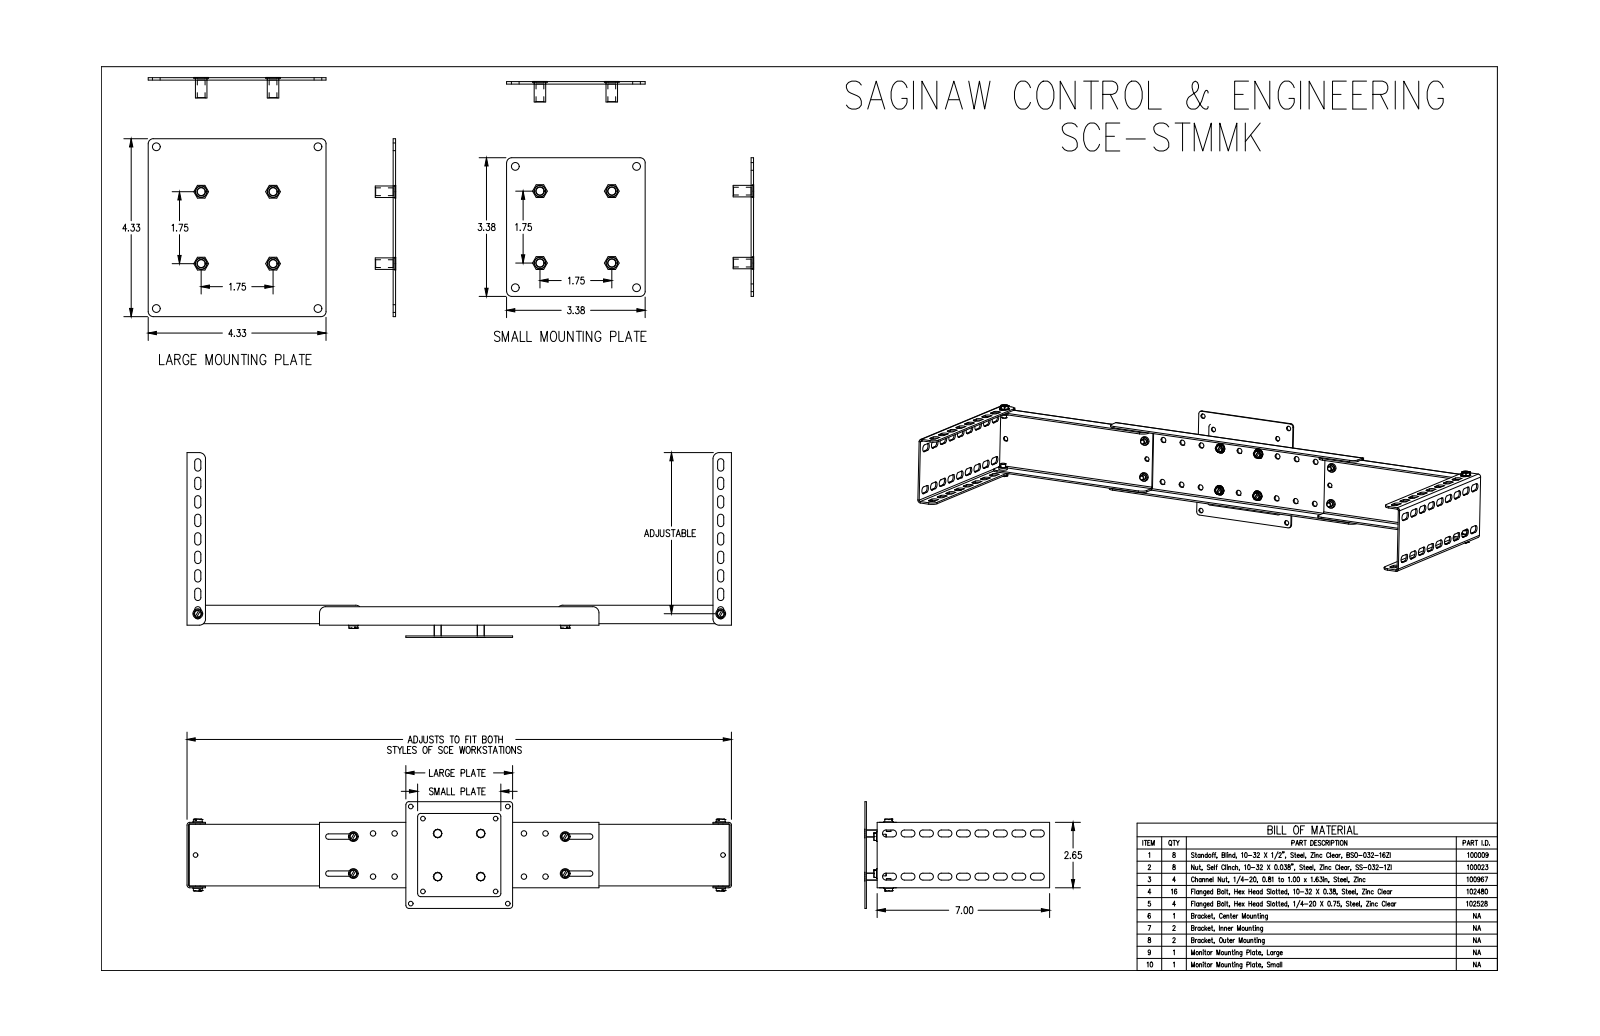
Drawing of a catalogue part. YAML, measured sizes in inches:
part_name: "SCE-STMMK"
step_written_by: "SolidWorks 2021 (AUTOMOTIVE_DESIGN)"
units: inches
bodies: {solids: 39, faces: 1196, planar: 574, cylindrical: 446, other: 176}
overall_size: [22.1, 7.5, 4.331]
volume: 10.82
surface_area: 379.9
round_holes:
  - {diameter: 0.218, count: 18}
  - {diameter: 0.19, count: 12}
  - {diameter: 0.266, count: 10}
  - {diameter: 0.187, count: 8}
  - {diameter: 0.25, count: 6}
  - {diameter: 0.281, count: 6}
  - {diameter: 0.187, count: 4}
round_bosses_or_shafts:
  - {diameter: 0.396, count: 10}
  - {diameter: 0.188, count: 10}
  - {diameter: 0.34, count: 6}
  - {diameter: 0.28, count: 6}
  - {diameter: 0.249, count: 6}
partial_cylinders:
  - {radius: 0.01, count: 60}
  - {radius: 0.125, count: 44}
  - {radius: 0.141, count: 36}
  - {radius: 0.25, count: 10}
  - {radius: 0.052, count: 8}
  - {radius: 0.109, count: 8}
  - {radius: 0.112, count: 8}
face_to_face_distances: [0.06, 0.06, 0.556, 0.616, 0.496, 22.04, 0.077, 2.517, 0.12, 0.436]
hole_center_spacings: [1.956, 2.474, 1.75, 1.75, 0.875, 0.875, 2.427, 2.625]
